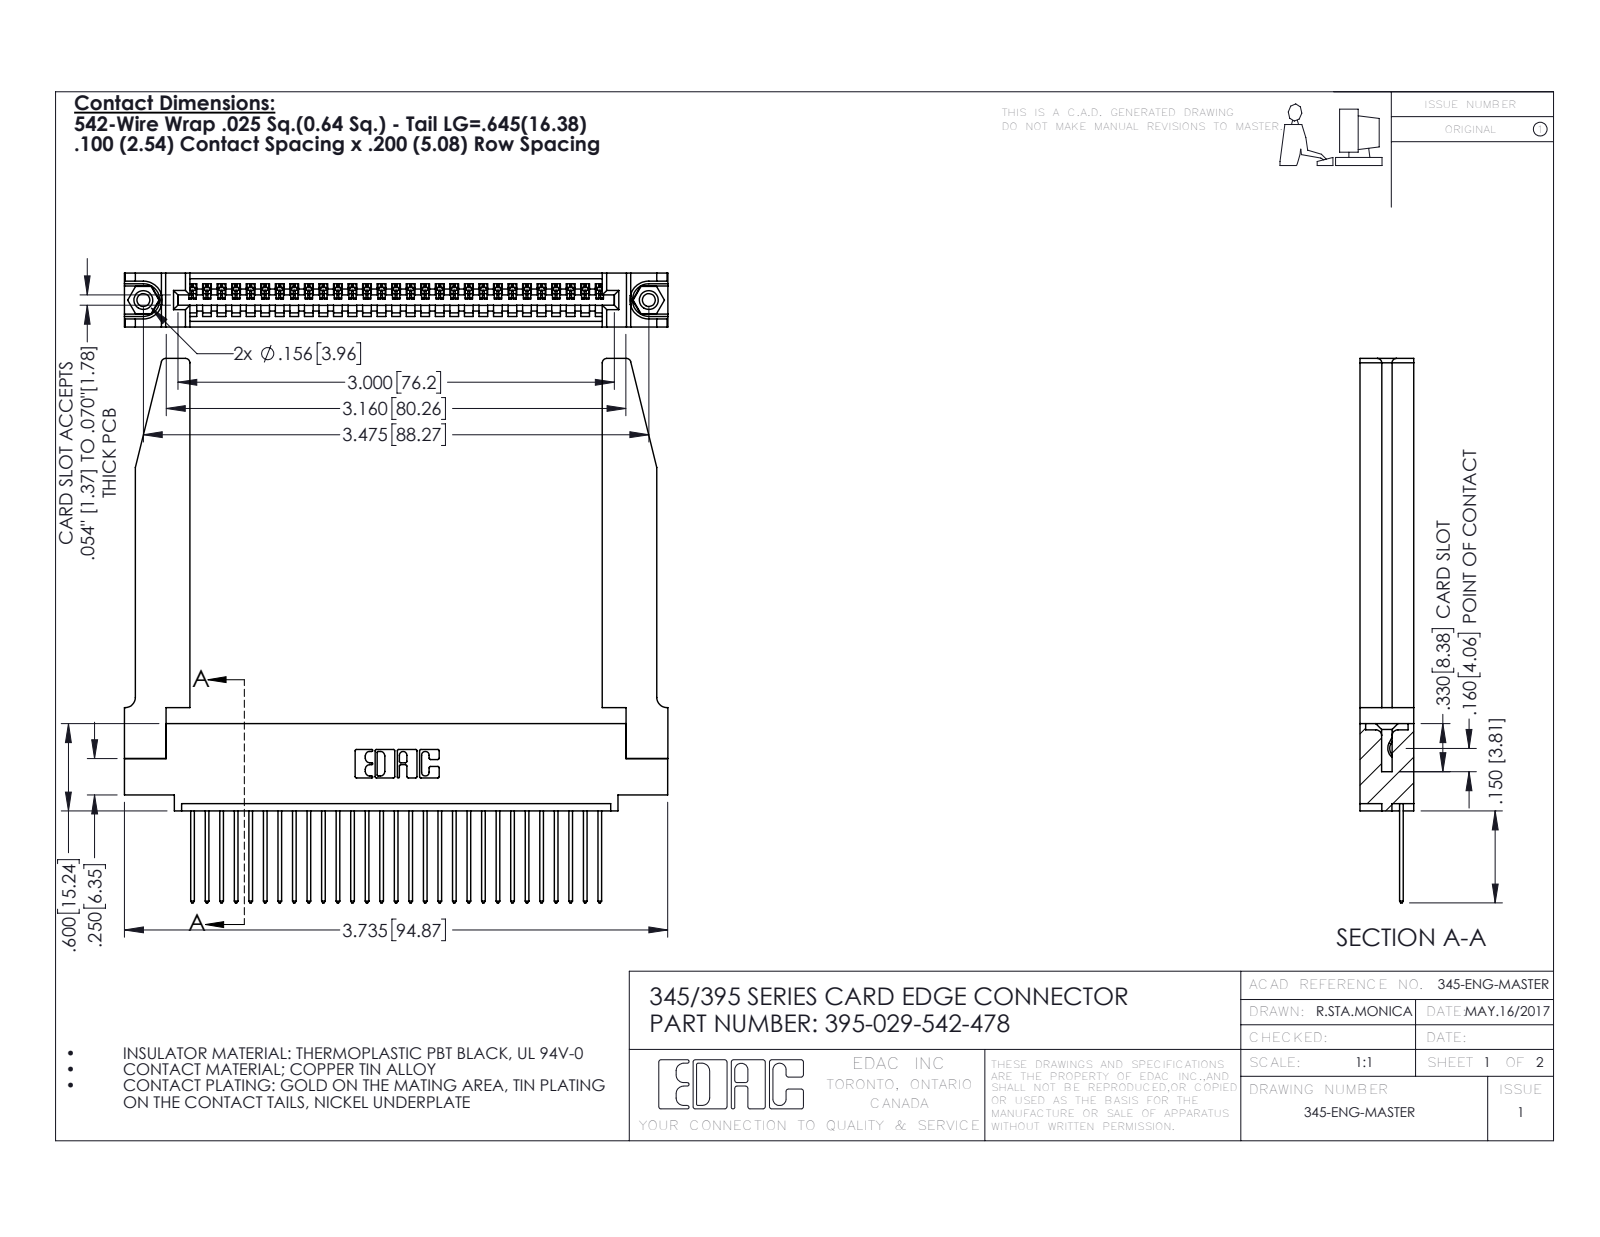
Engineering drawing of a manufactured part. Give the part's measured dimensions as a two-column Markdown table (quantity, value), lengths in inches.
| quantity | value |
| --- | --- |
| part name | 345-220-078_345-220-078; 395-029-542-478; 345-250-001_345-250-001-102; 345-292-001_345-293-142 (+1 more) |
| STEP written by | SolidWorks 2016 (CONFIG_CONTROL_DESIGN) |
| units | inches |
| bodies | 34 solids, 2046 faces (1386 planar, 608 cylindrical, 52 other) |
| overall size | 3.742 × 3.736 × 0.37 |
| volume | 1.017 in³ |
| surface area | 29.42 in² |
| round holes (diameter × count) | 0.089 × 2, 0.125 × 2, 0.156 × 2, 0.064 × 1 |
| round bosses / shafts (diameter × count) | 0.155 × 2 |
| partial cylindrical surfaces (radius × count) | 0.006 × 58, 0.01 × 58, 0.01 × 22, 0.03 × 8, 0.007 × 6, 0.031 × 6, 0.026 × 3, 0.031 × 2 |
| main face-to-face distances | 0.37, 0.072, 0.298, 0.098, 0.272, 0.025, 0.2, 0.148, 0.15, 0.225 |
| hole center spacings | 0.27, 3.24, 3.475 |
